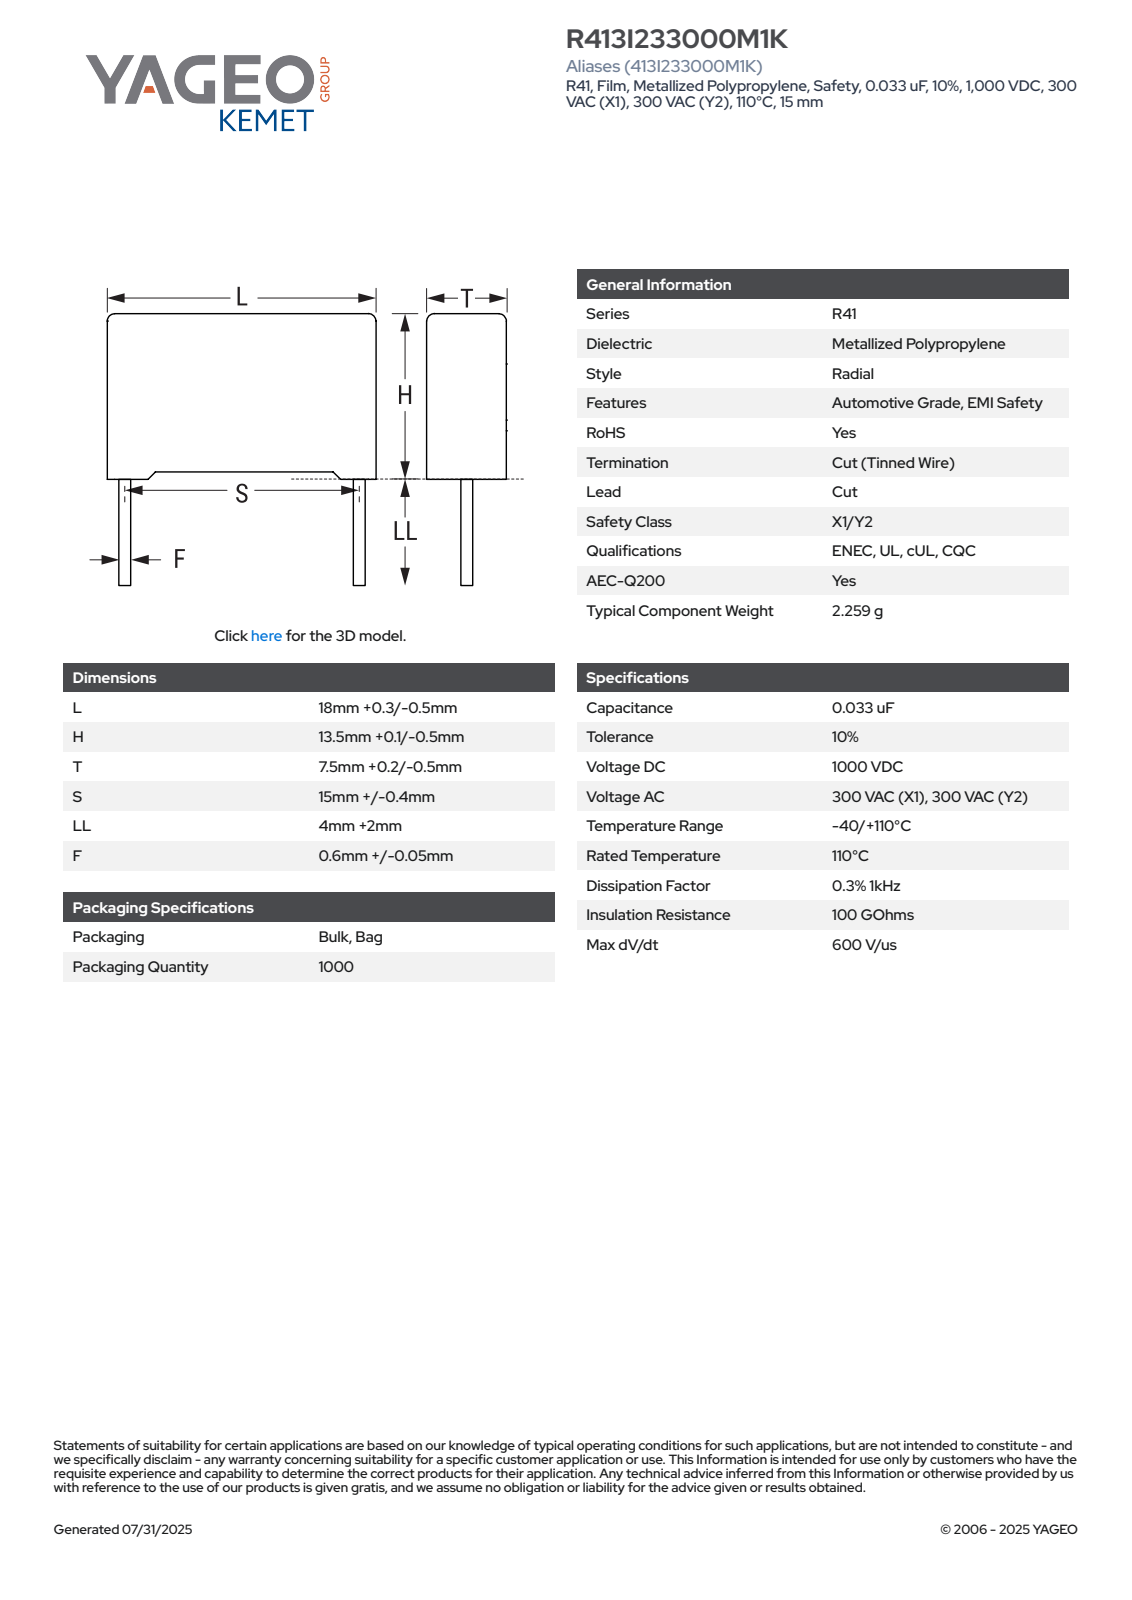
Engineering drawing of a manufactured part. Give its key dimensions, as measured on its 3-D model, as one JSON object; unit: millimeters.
{"part_name": "CFR_RB2_18X13.5X7.5_L18.3H13.6T7.7S15LL6F0.65", "step_written_by": "SolidWorks 2021 (AUTOMOTIVE_DESIGN)", "units": "millimeters", "bodies": {"solids": 4, "faces": 85, "planar": 77, "cylindrical": 8, "other": 0}, "overall_size": [19.6, 18.3, 7.71], "volume_mm3": 1829, "surface_area_mm2": 1045, "round_bosses_or_shafts": [[0.65, 2]], "partial_cylinders_radius": [[0.5, 4]], "face_to_face_distances": [7.7, 12.85, 18.3, 0.61, 0.75, 13.6, 7.09, 13.13, 0.47, 17.69]}
